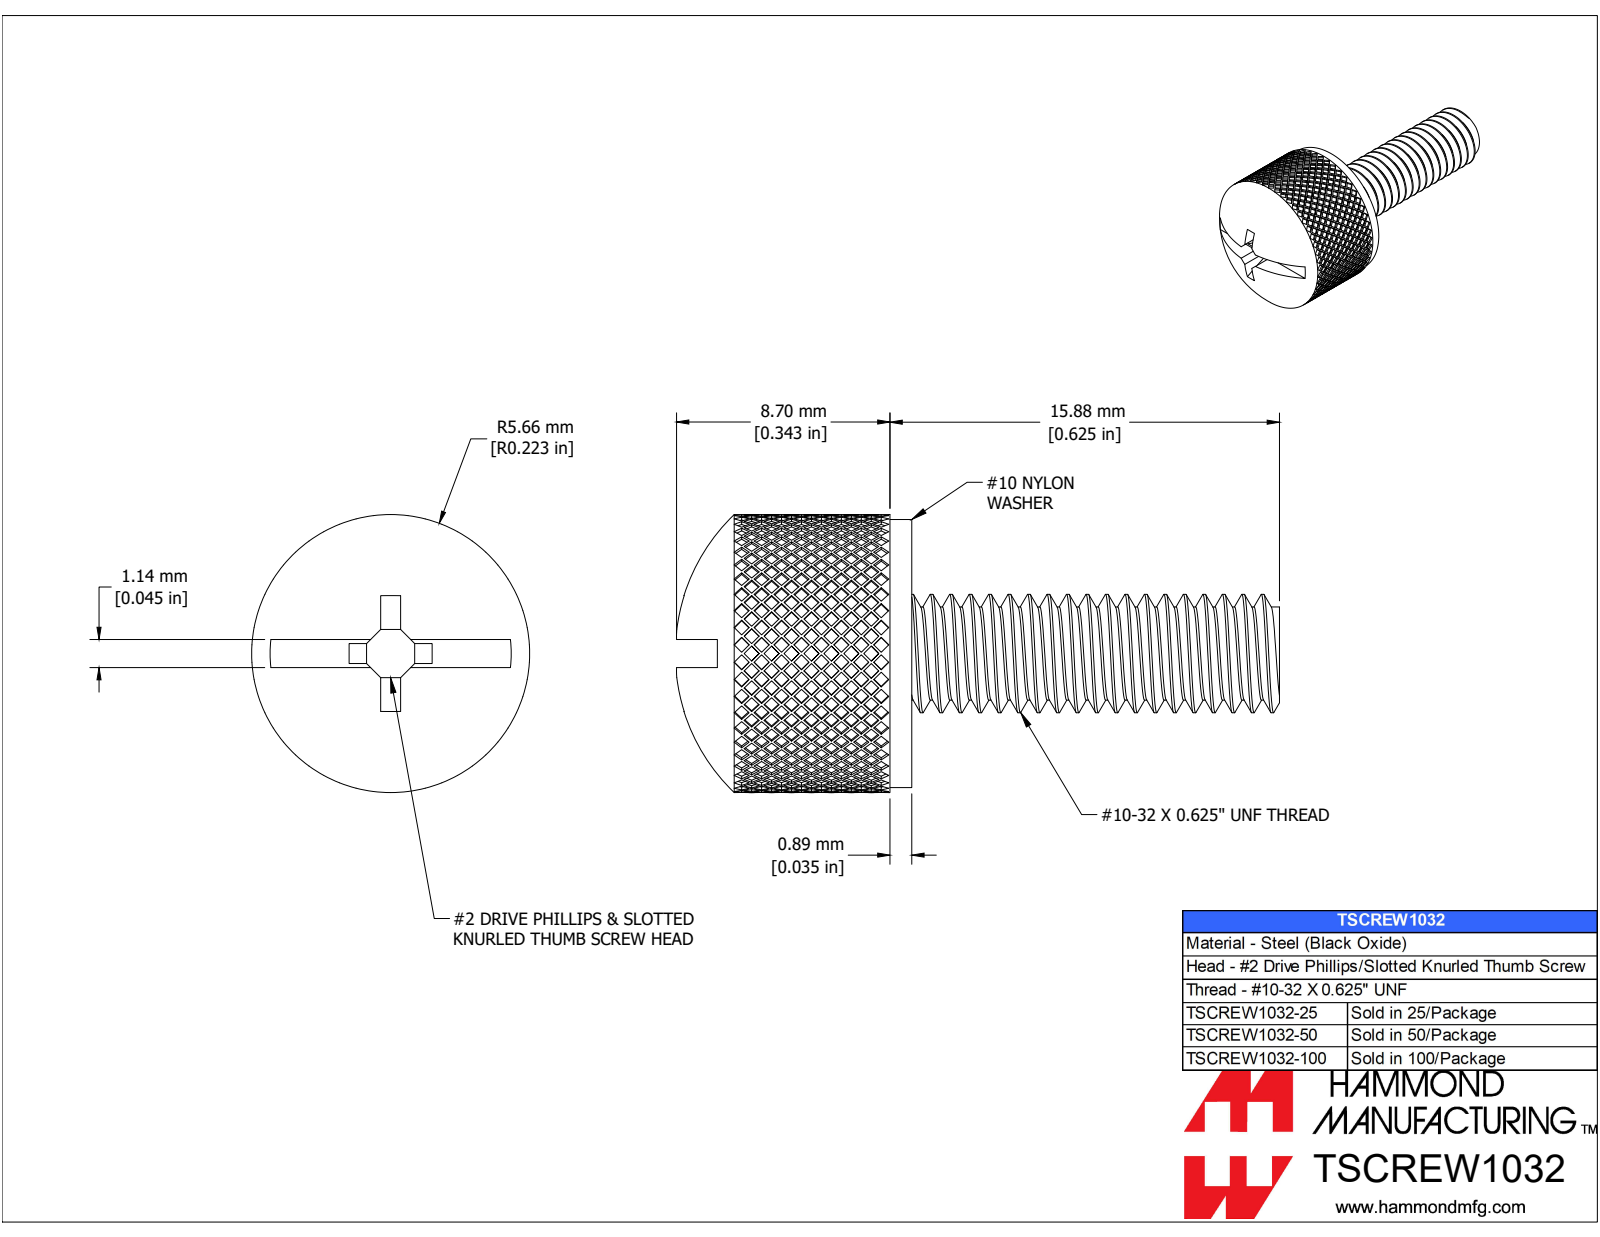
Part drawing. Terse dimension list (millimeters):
name: TSCREW1032-50
written by: SolidWorks 2019 (CONFIG_CONTROL_DESIGN)
unit: mm
bodies: 3 solids, 3789 faces (3778 planar, 5 cylindrical, 6 other)
size: 24.6 × 11.3 × 11.3
volume: 1 000 mm³; area: 1 210 mm²
holes: 1× ⌀5.1
bosses: 1× ⌀11.3, 1× ⌀10.9, 1× ⌀4.8, 1× ⌀3.8
face distances: 1.1, 0.9, 0.6, 0.4, 2.3, 0.6, 1.7, 1.6, 0.7, 11.1
